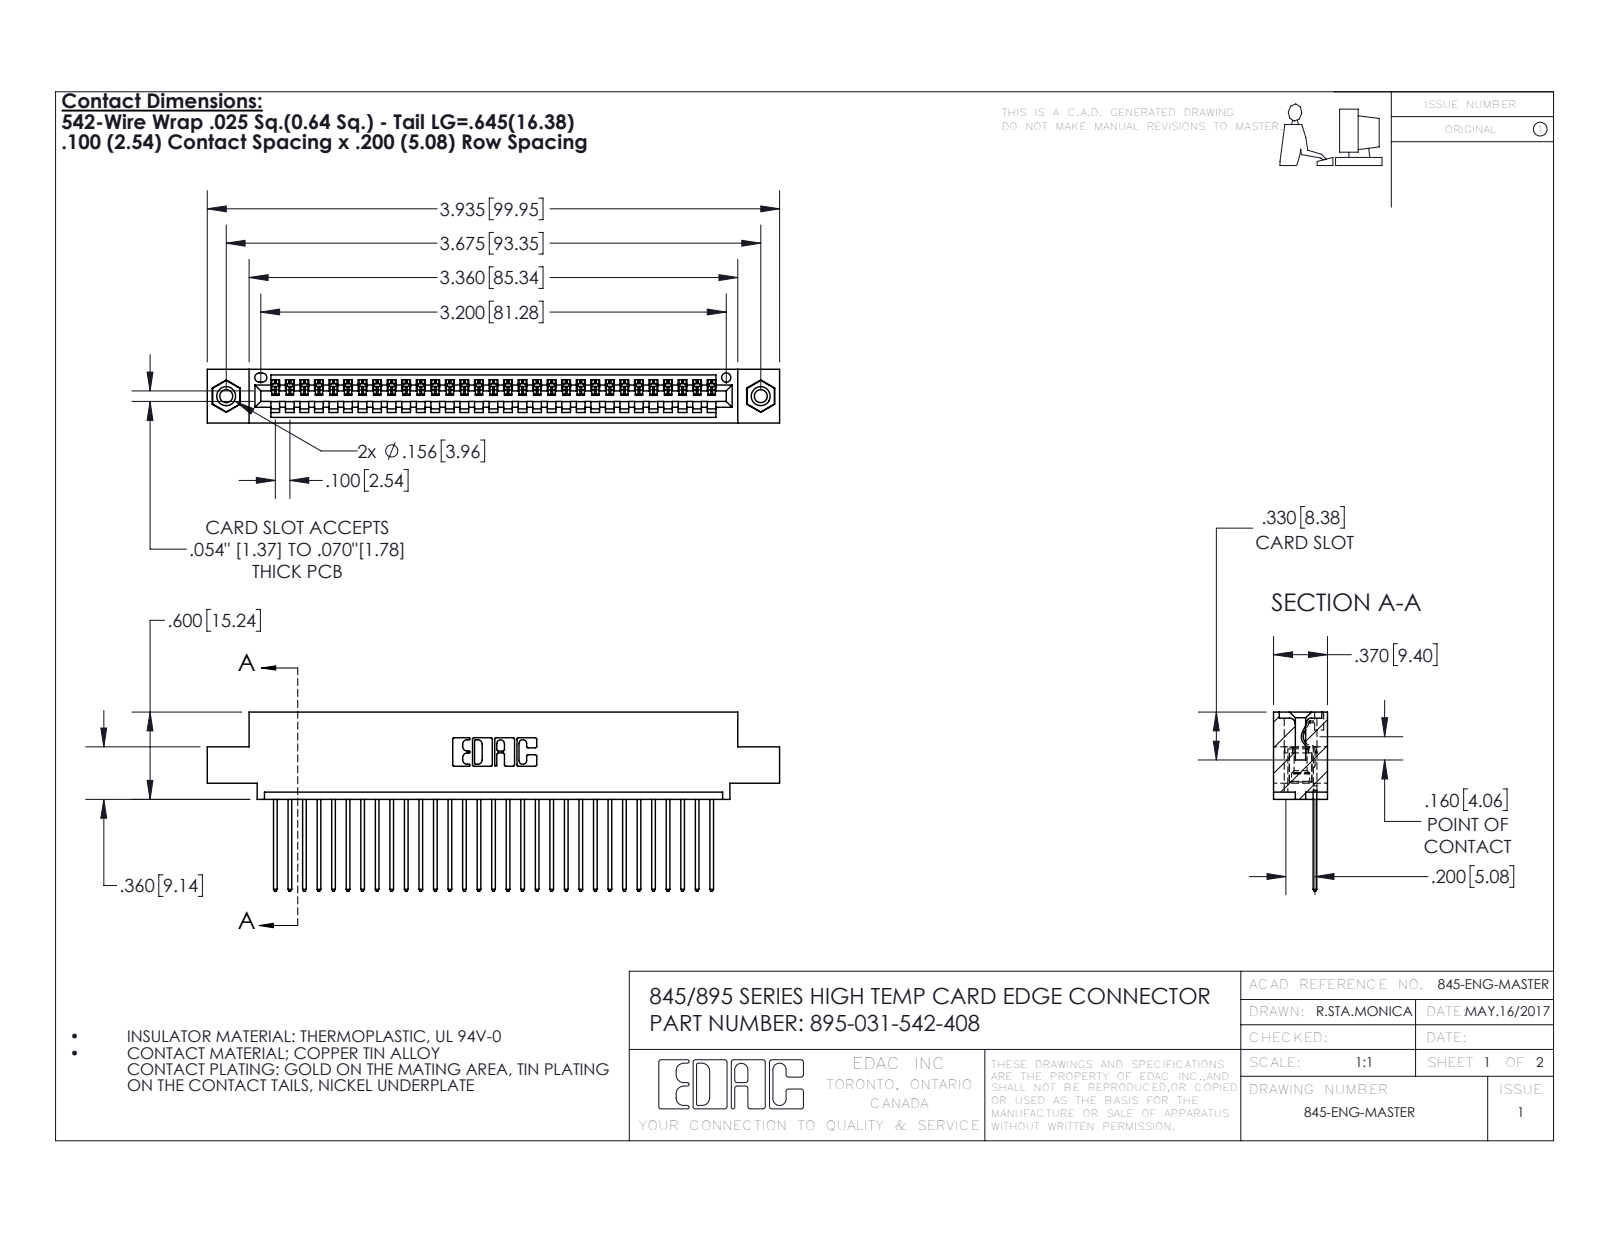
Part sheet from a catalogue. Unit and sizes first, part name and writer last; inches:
Units: inches
Overall size (bounding box): 3.935 × 1.232 × 0.37
Round holes (diameter × count): ⌀0.089 ×2, ⌀0.125 ×2, ⌀0.156 ×2, ⌀0.064 ×1
Round bosses / shafts (diameter × count): ⌀0.155 ×2
Partial cylindrical surfaces — rounded edges, fillets, slot ends (radius × count): R0.006 ×62, R0.01 ×62, R0.01 ×22, R0.007 ×6, R0.031 ×6, R0.026 ×3, R0.031 ×2, R0.04 ×2
Main face-to-face distances: 0.072, 0.298, 0.37, 0.2, 0.098, 0.272, 0.025, 0.225, 0.149, 0.072
Hole centre spacings: 0.27, 3.44, 3.675
Volume: 0.573 in³ · Surface area: 19.95 in²
Bodies: 34 solids, 1988 faces (1356 planar, 616 cylindrical, 16 other)
Part name (STEP PRODUCT): 395-031-542-408; 345-292-001_345-293-142; 345-250-001_345-250-003-102; 345 Part_0.110 Offset - 0.156 Dia-TI
STEP written by: SolidWorks 2016 (CONFIG_CONTROL_DESIGN)
